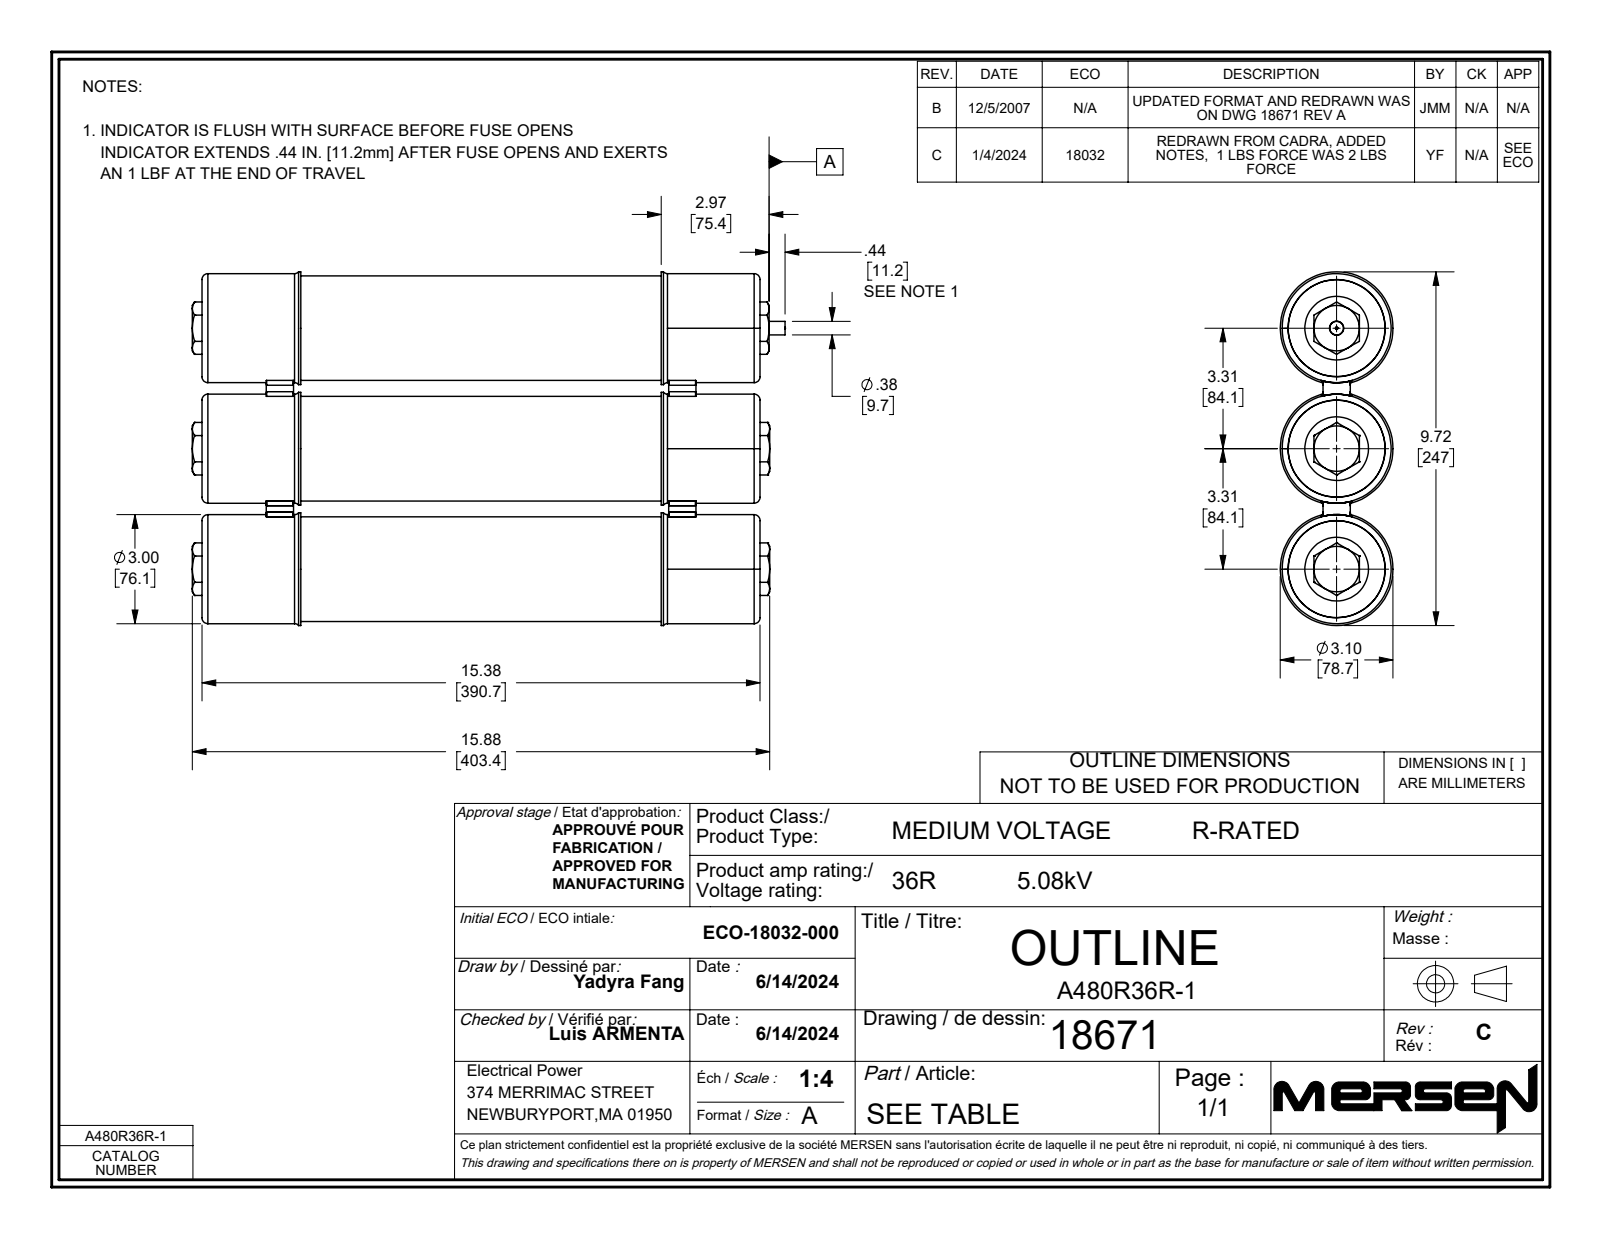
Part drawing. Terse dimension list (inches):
name: Copy of 919509943^360032; 340012_-001 SET; Copy of Copy of 979103557^360033; Copy of 979103557^360032 (+8 more)
written by: SolidWorks 2021 (AUTOMOTIVE_DESIGN)
unit: in
bodies: 37 solids, 997 faces (339 planar, 350 cylindrical, 308 other)
size: 15.88 × 9.724 × 3.1
volume: 64.46 in³; area: 1 228 in²
holes: 3× ⌀0.906, 3× ⌀2.625, 3× ⌀2.89, 2× ⌀2.998, 1× ⌀0.02, 1× ⌀0.063, 1× ⌀0.146, 1× ⌀0.188, 1× ⌀0.391, 1× ⌀0.465, 1× ⌀0.512
bosses: 3× ⌀3.1, 3× ⌀2.875, 3× ⌀1.25, 3× ⌀0.78, 3× ⌀0.125, 2× ⌀0.9, 1× ⌀2.998, 1× ⌀0.875
rounds: 8× R0.032, 8× R0.187, 7× R4, 3× R1.5
face distances: 15.224, 0.019, 15.097, 0.382, 15.498, 0.401, 15.479, 0.054, 15.17, 15.116
hole spacings: 3.312, 3.312, 6.624
